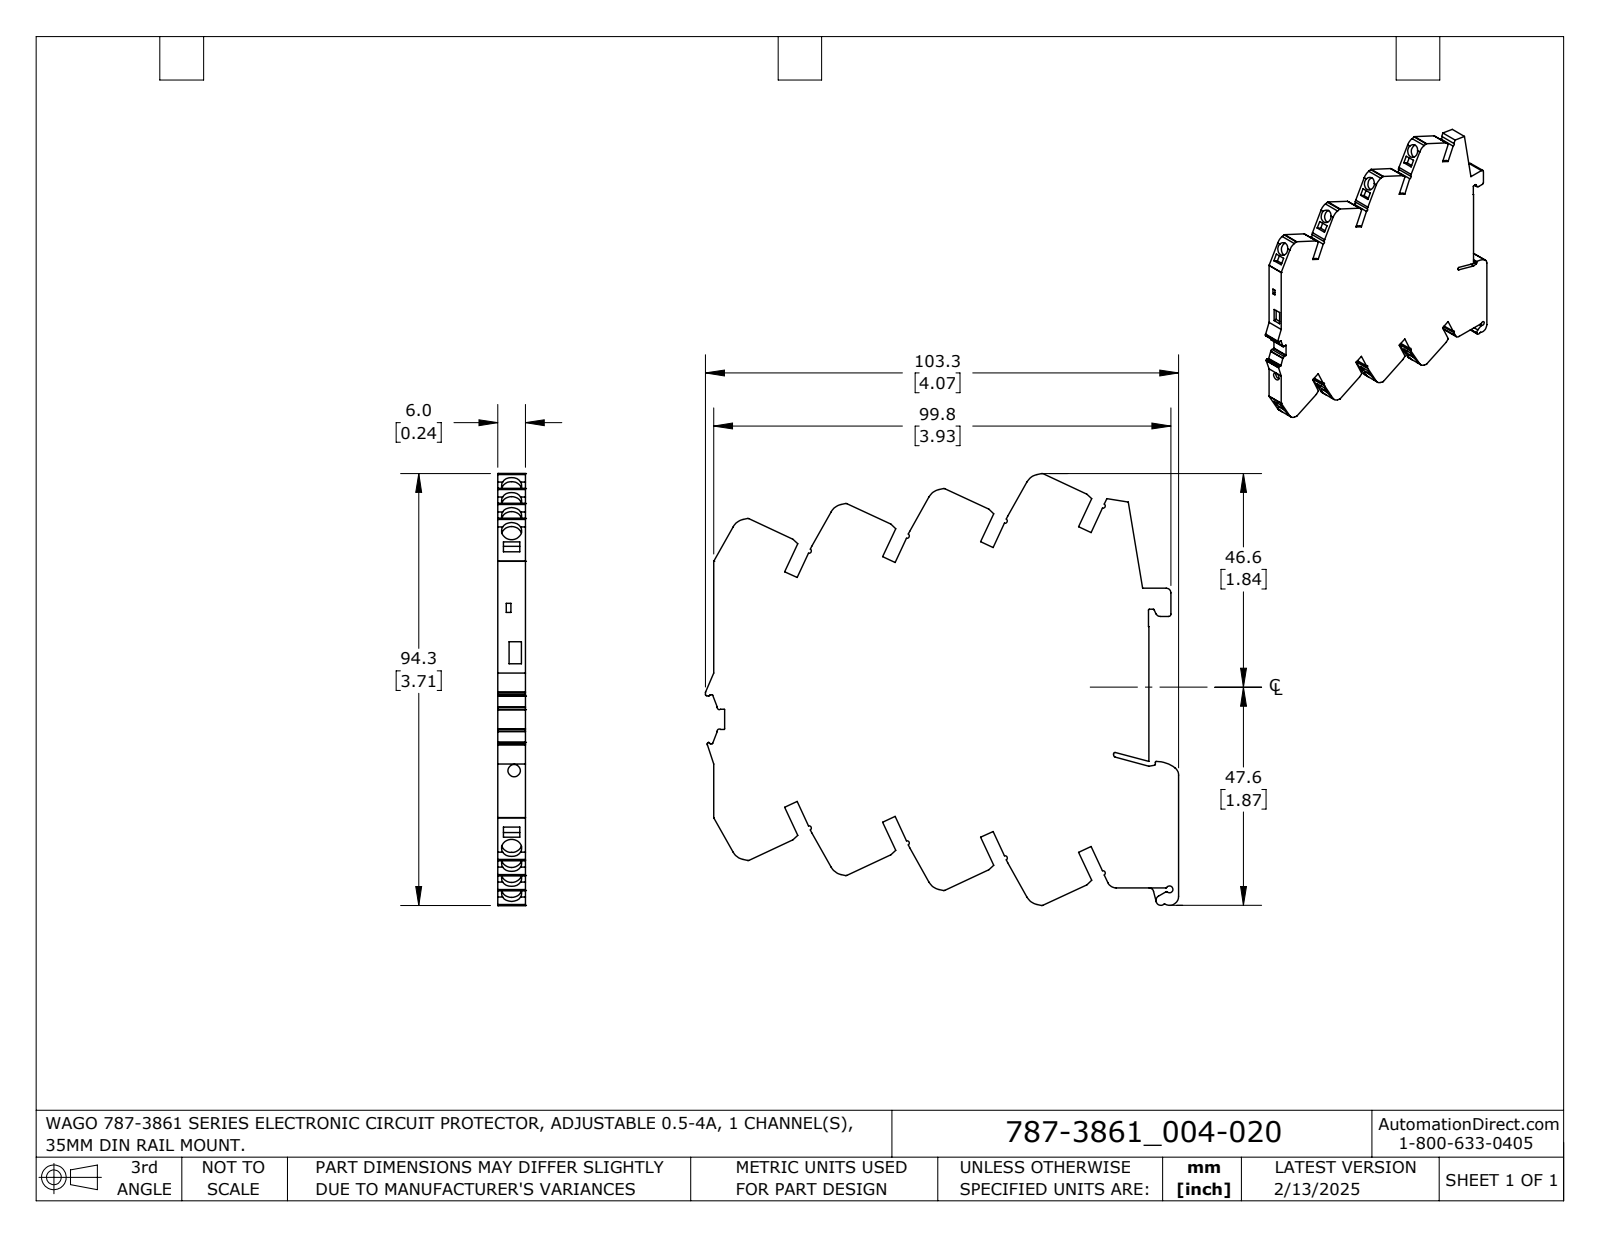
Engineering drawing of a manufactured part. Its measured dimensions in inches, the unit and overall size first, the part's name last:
Units: inches
Overall size (bounding box): 4.067 × 3.711 × 0.236
Round holes (diameter × count): ⌀0.173 ×8, ⌀0.106 ×1
Partial cylindrical surfaces — rounded edges, fillets, slot ends (radius × count): R0.008 ×13, R0.02 ×12, R0.016 ×8, R0.132 ×8, R0.039 ×5, R0.012 ×3, R0.079 ×3, R0.018 ×2
Main face-to-face distances: 0.236, 0.708, 0.67, 1.417, 0.118, 0.473, 0.826, 0.472, 1.34, 1.535
Hole centre spacings: 0.526, 0.525, 1.051, 1.052, 1.577
Volume: 2.684 in³ · Surface area: 29.26 in²
Bodies: 1 solid, 267 faces (202 planar, 65 cylindrical, 0 other)
Part name (STEP PRODUCT): 787-3861_004-020_HI
STEP written by: SolidWorks 2024 (AUTOMOTIVE_DESIGN)
